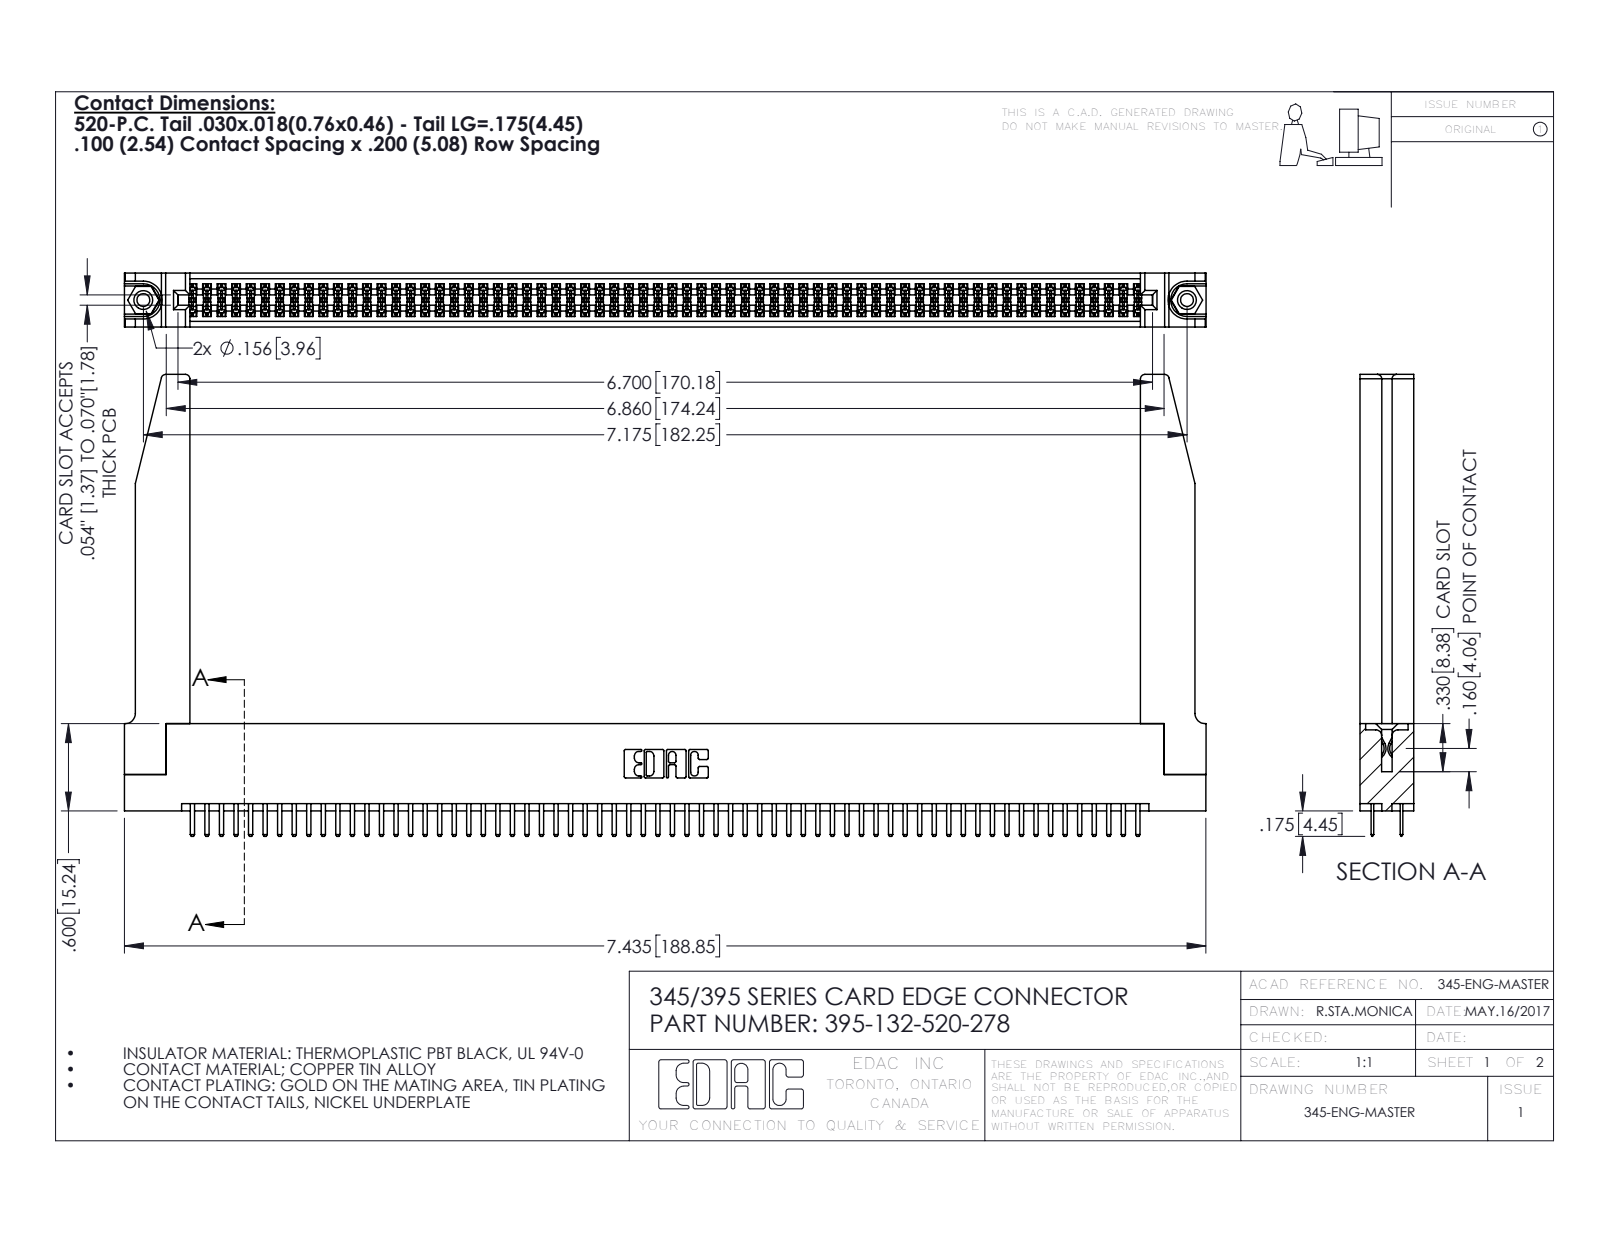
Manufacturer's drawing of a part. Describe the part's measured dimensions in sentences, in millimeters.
The part is named "345-250-001_345-250-001-102; 395-132-520-278; 345-220-078_345-220-078; 345-292-001_345-293-120 (+1 more)". Its 3-D file was written by "SolidWorks 2016 (CONFIG_CONTROL_DESIGN)". It is 137 solids with 7488 faces: 4842 planar, 2594 cylindrical and 52 other. Overall it measures 188.9 by 80.6 by 9.4 millimeters. Its volume is 26 280 cubic millimeters and its surface area 34 540 square millimeters. Round holes: 2 of diameter 2.3, 2 of diameter 3.2, 2 of diameter 4, 1 of diameter 1.6. Round bosses or shafts: 2 of diameter 3.9. Partial cylindrical surfaces (rounded edges, fillets, slot ends): 198 of radius 0.2, 136 of radius 0.3, 22 of radius 0.3, 8 of radius 0.8, 6 of radius 0.2, 6 of radius 0.8, 3 of radius 0.7, 2 of radius 0.4. The main face-to-face distances are 1.8, 7.6, 9.4, 5.1, 2.5, 6.9, 0.6, 5.7, 0.6, 1.8. The hole center spacings are 6.9, 176.3, 182.2.
